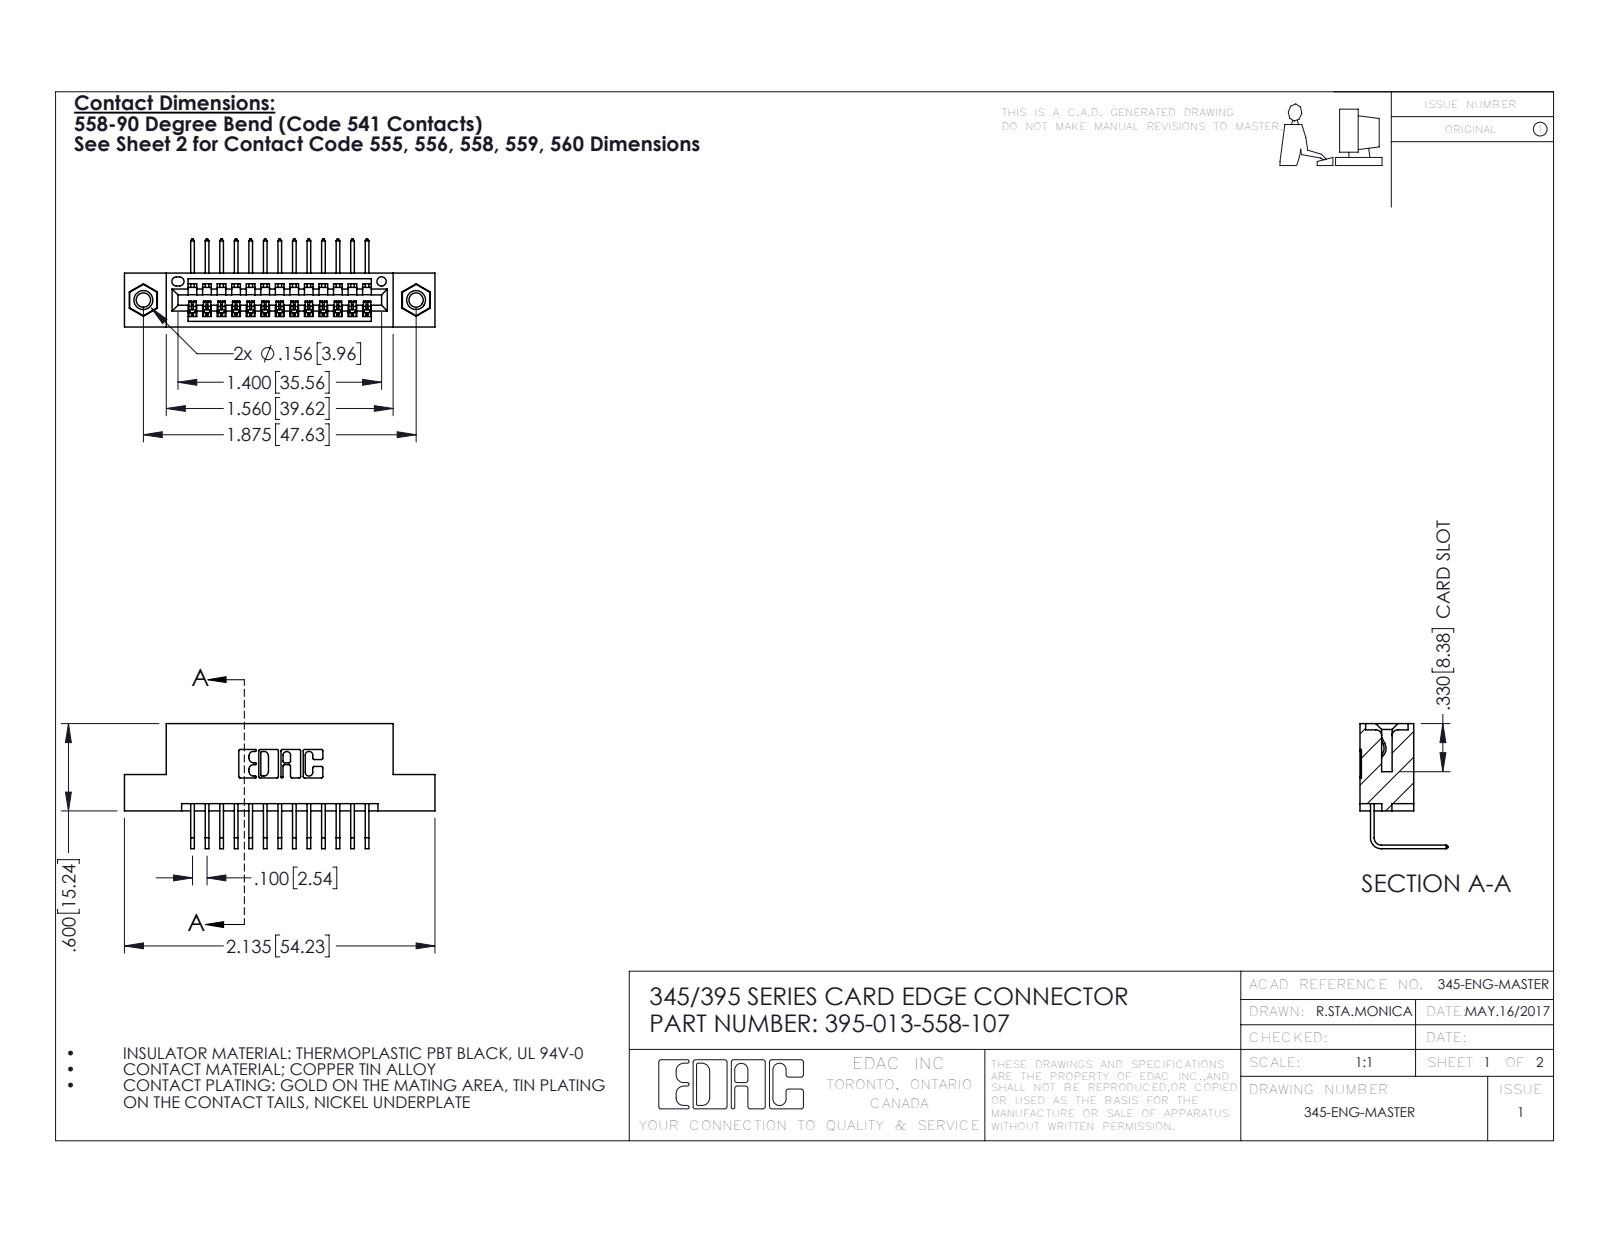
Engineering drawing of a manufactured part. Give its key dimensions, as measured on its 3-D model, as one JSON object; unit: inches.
{"part_name": "345-250-001_345-250-005-103; 345 Part_Flush Mounting Lugs - 0.156 Dia-TI; 395-013-558-107; 345-292-001_558 Tail - 2", "step_written_by": "SolidWorks 2016 (CONFIG_CONTROL_DESIGN)", "units": "inches", "bodies": {"solids": 16, "faces": 966, "planar": 658, "cylindrical": 292, "other": 16}, "overall_size": [2.135, 0.859, 0.605], "volume_in3": 0.302, "surface_area_in2": 10.02, "round_holes": [[0.098, 2], [0.125, 2], [0.156, 2], [0.064, 1]], "round_bosses_or_shafts": [[0.155, 2]], "partial_cylinders_radius": [[0.006, 26], [0.01, 22], [0.007, 6], [0.031, 6], [0.026, 3], [0.031, 2], [0.04, 2], [0.014, 1]], "face_to_face_distances": [0.2, 0.072, 0.298, 0.37, 0.098, 0.272, 0.025, 0.1, 0.225, 0.3], "hole_center_spacings": [0.27, 1.643, 1.875]}
